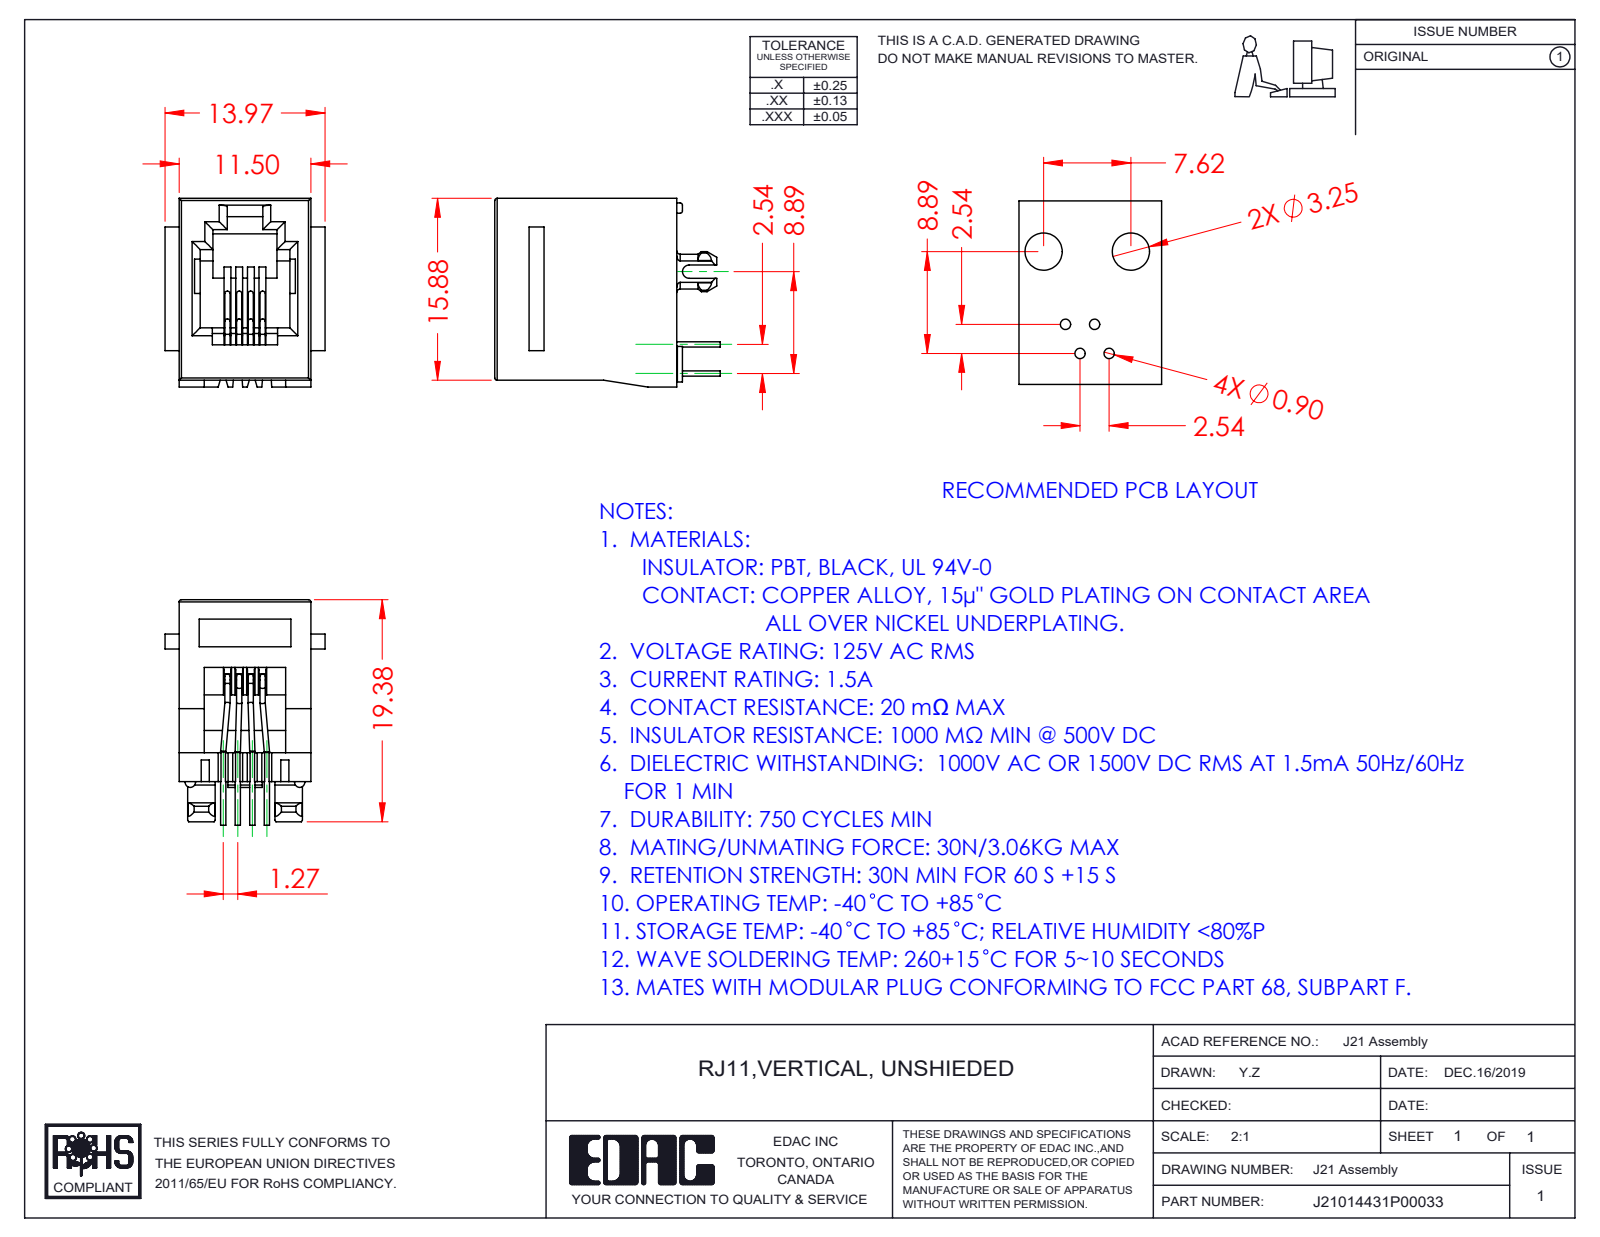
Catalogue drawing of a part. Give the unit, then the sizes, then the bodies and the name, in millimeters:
Units: millimetres
Overall size (bounding box): 19.68 × 16.48 × 13.97
Round holes (diameter × count): ⌀2 ×2
Round bosses / shafts (diameter × count): ⌀0.46 ×24
Partial cylindrical surfaces — rounded edges, fillets, slot ends (radius × count): R0.5 ×9, R0.7 ×9, R0.2 ×7, R0.23 ×4, R0.45 ×2, R1.52 ×2, R1.75 ×2, R0.57 ×1
Main face-to-face distances: 11.5, 1.6, 15.88, 1.02, 7.2, 0.6, 2.95, 8.55, 2.04, 1.35
Hole centre spacings: 8.4
Volume: 1 616 mm³ · Surface area: 2 564 mm²
Bodies: 5 solids, 369 faces (230 planar, 111 cylindrical, 28 other)
Part name (STEP PRODUCT): 21 Contacts; 21 Insulator; RJ21014431P00033
STEP written by: SolidWorks 2016 (CONFIG_CONTROL_DESIGN)
